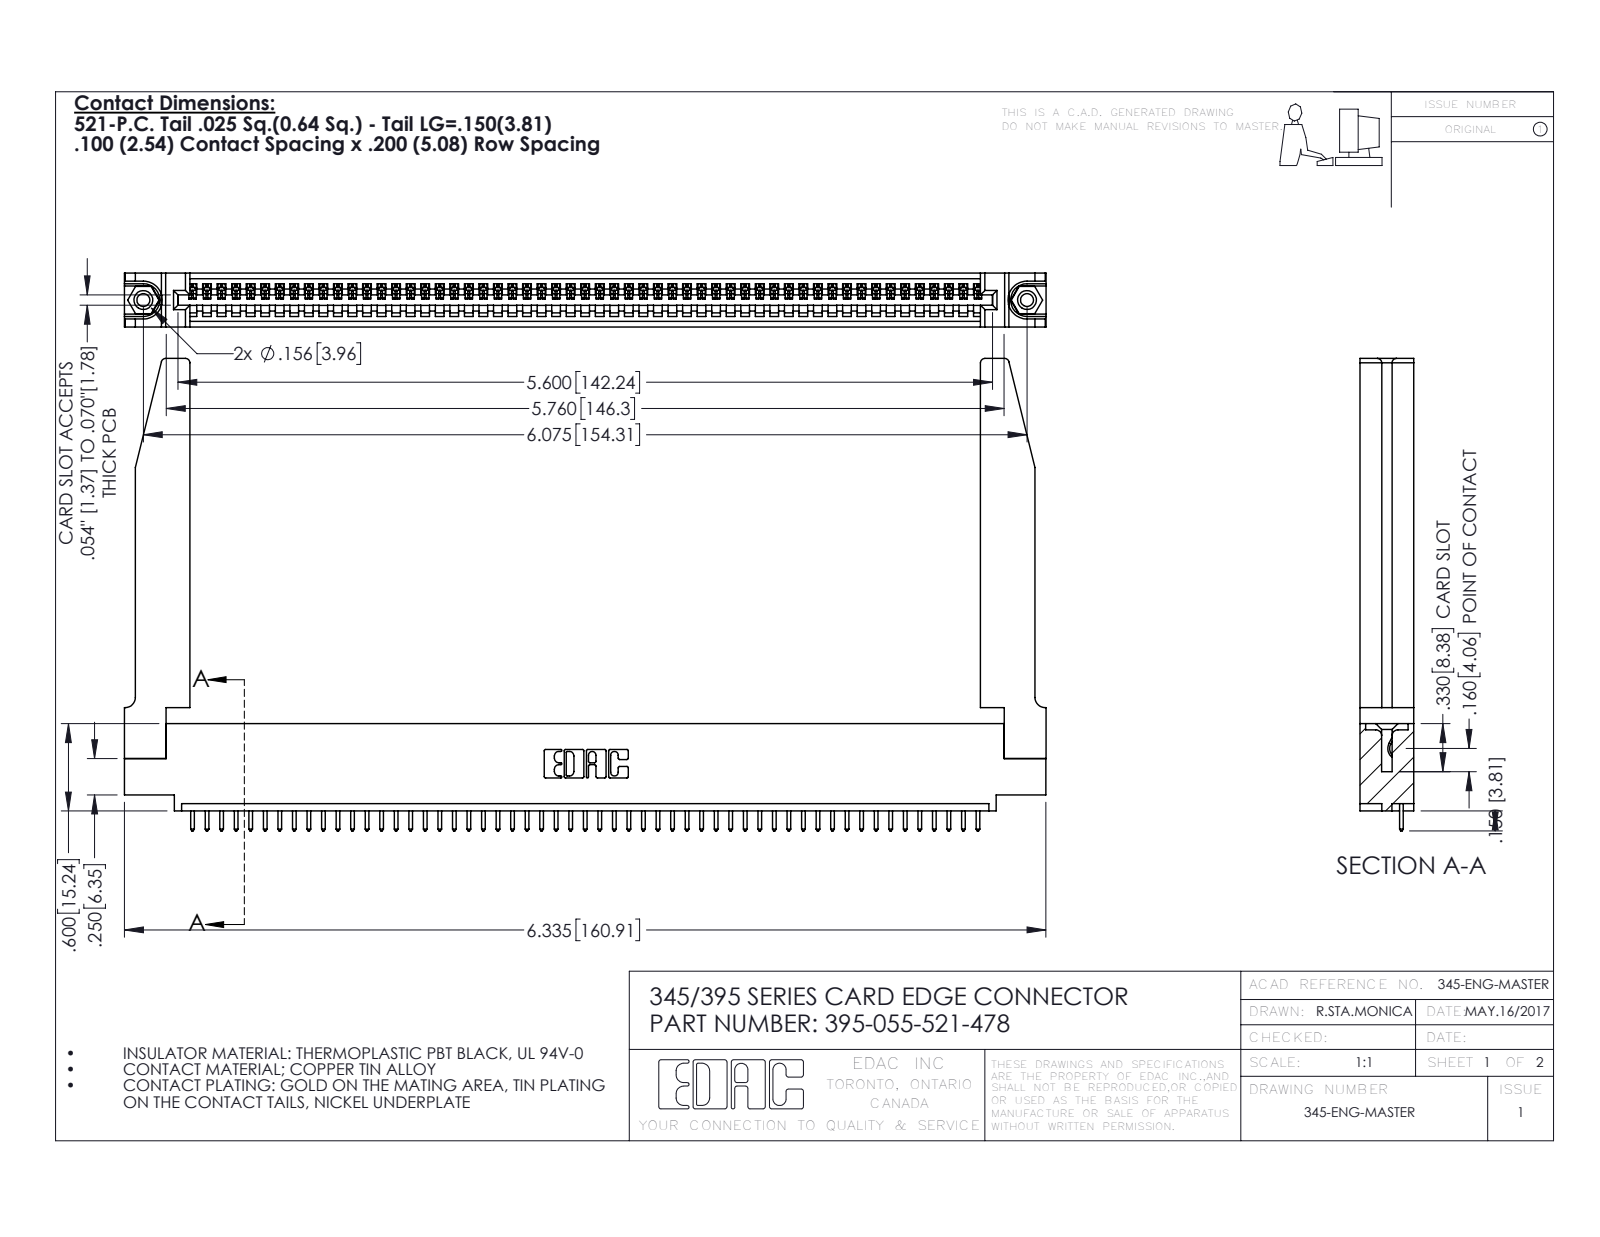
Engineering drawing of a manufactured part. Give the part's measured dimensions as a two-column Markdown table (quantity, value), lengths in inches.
| quantity | value |
| --- | --- |
| part name | 345-292-001_345-293-121; 345 Part_0.110 Offset - 0.156 Dia-TH; 395-055-521-478; 345-250-001_345-250-001-102 (+1 more) |
| STEP written by | SolidWorks 2016 (CONFIG_CONTROL_DESIGN) |
| units | inches |
| bodies | 60 solids, 3554 faces (2426 planar, 1076 cylindrical, 52 other) |
| overall size | 6.336 × 3.247 × 0.37 |
| volume | 1.399 in³ |
| surface area | 41.29 in² |
| round holes (diameter × count) | 0.089 × 2, 0.125 × 2, 0.156 × 2, 0.064 × 1 |
| round bosses / shafts (diameter × count) | 0.155 × 2 |
| partial cylindrical surfaces (radius × count) | 0.006 × 110, 0.01 × 110, 0.01 × 22, 0.03 × 8, 0.007 × 6, 0.031 × 6, 0.026 × 3, 0.031 × 2 |
| main face-to-face distances | 0.37, 0.072, 0.298, 0.2, 0.098, 0.272, 0.025, 0.225, 0.148, 0.15 |
| hole center spacings | 0.27, 5.839, 6.075 |
